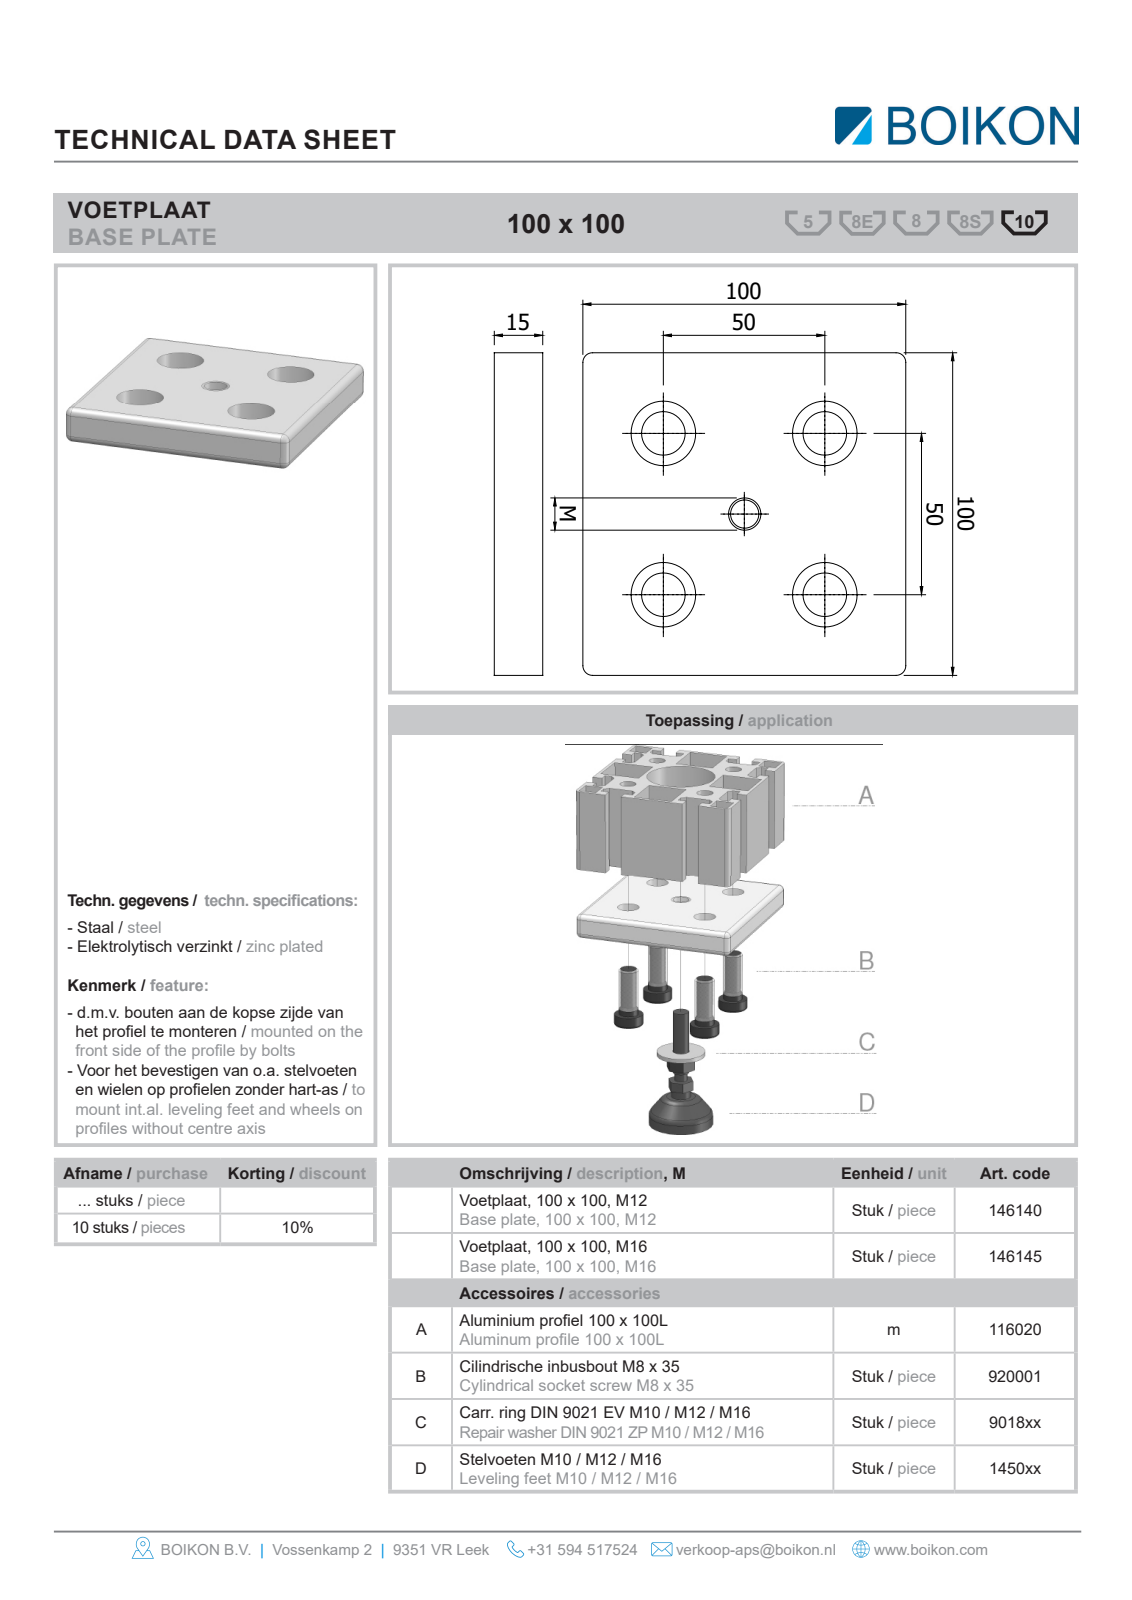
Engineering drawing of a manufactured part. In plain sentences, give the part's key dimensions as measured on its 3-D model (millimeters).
The part is named "Root; 146145Voetplaat 100x100 M16BOIKON3*; 920001Cil. inb. M12 x 30, DIN 7984 verk. kopBOIKON0". Its 3-D file was written by "HiCAD 2013 1802.4 Build 509 (AUTOMOTIVE_DESIGN)". It is 5 solids with 107 faces: 74 planar, 21 cylindrical and 12 other. Overall it measures 100 by 100 by 39 millimeters. Its volume is 147 807 cubic millimeters and its surface area 36 291 square millimeters. Round holes: 4 of diameter 13.5, 4 of diameter 20, 1 of diameter 16. Round bosses or shafts: 4 of diameter 18, 4 of diameter 12, 4 of diameter 9.85. The main face-to-face distances are 15, 100, 6, 9, 2, 7, 13, 24, 30, 37. The hole center spacings are 35.36, 50, 70.71.
